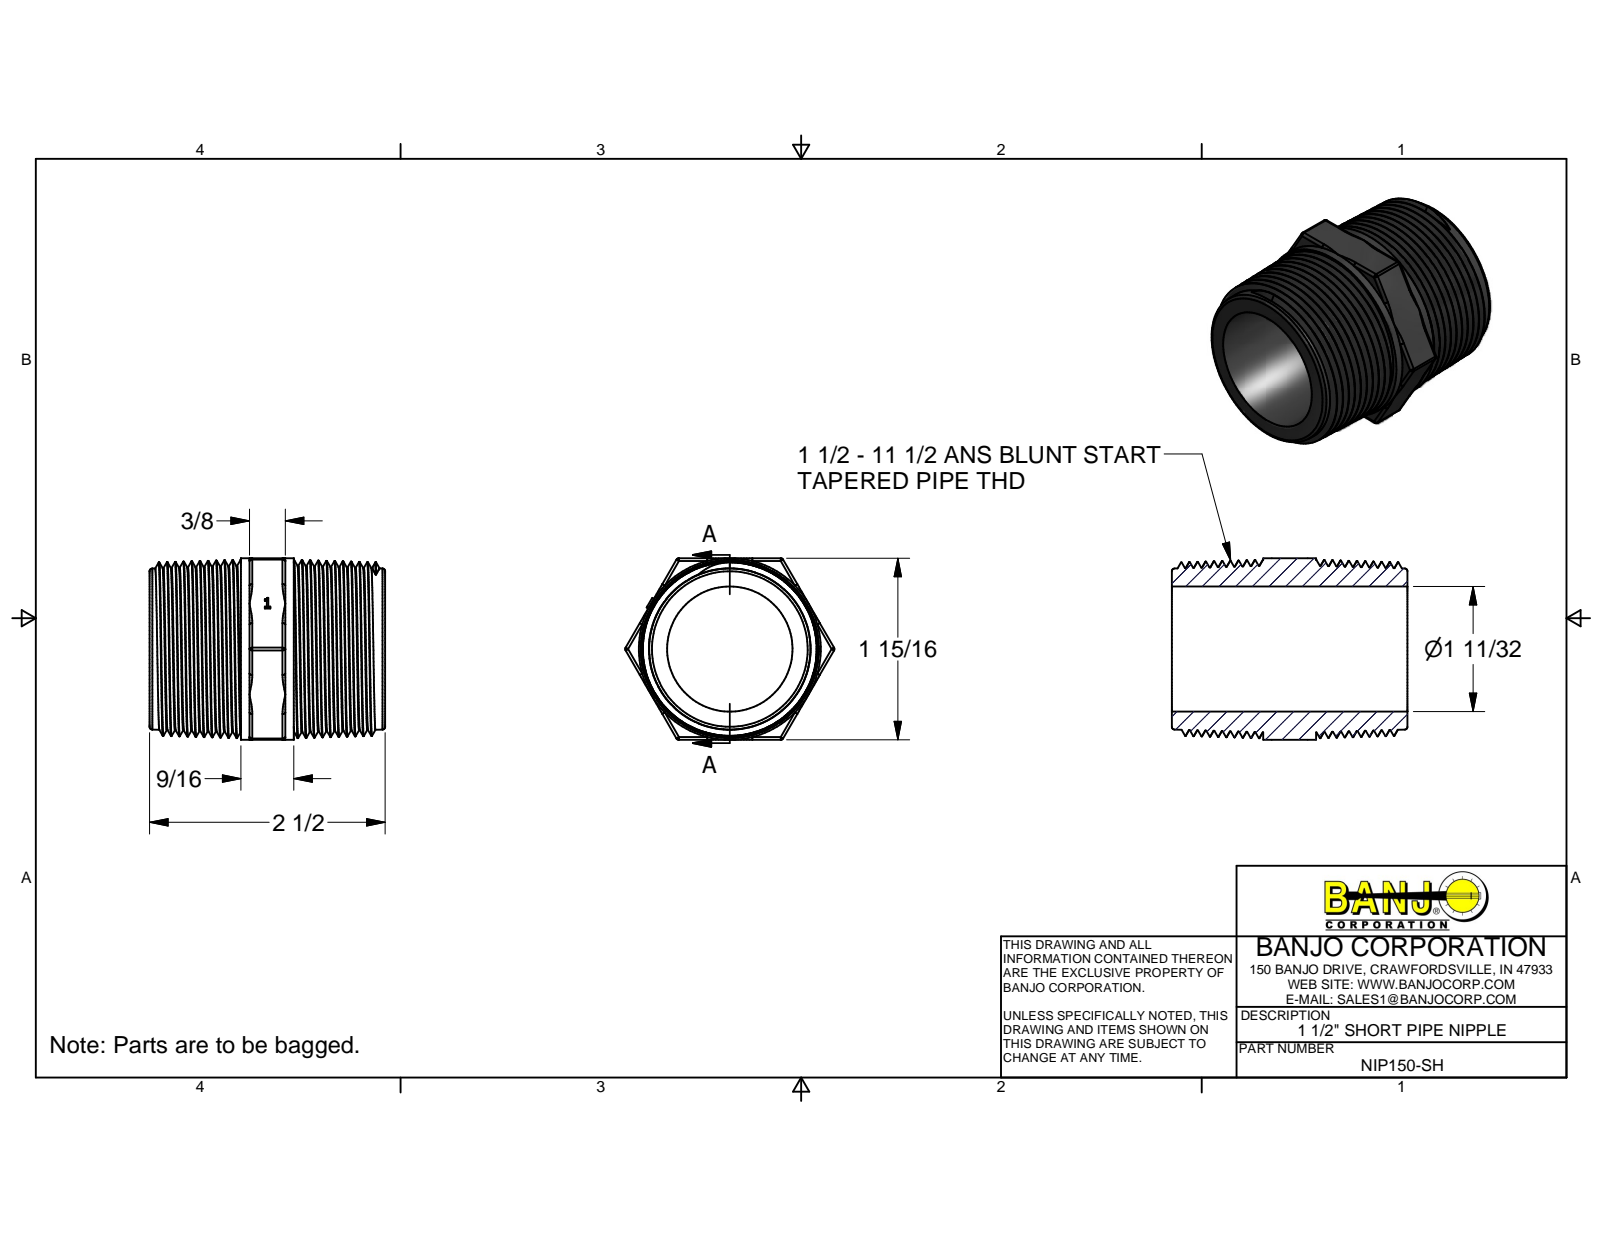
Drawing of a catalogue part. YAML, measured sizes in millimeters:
part_name: "NIP150-SH"
step_written_by: "Autodesk Inventor 2013 (AUTOMOTIVE_DESIGN)"
units: millimeters
bodies: {solids: 1, faces: 139, planar: 35, cylindrical: 33, other: 71}
overall_size: [63.5, 56.4, 49]
volume: 52260
surface_area: 23230
round_holes:
  - {diameter: 33.8, count: 1}
round_bosses_or_shafts:
  - {diameter: 49, count: 1}
partial_cylinders:
  - {radius: 0.8, count: 18}
face_to_face_distances: [49, 63.5, 24.6, 38.9, 26.9, 36.6, 2.3, 11.9, 14.2, 9.7]
